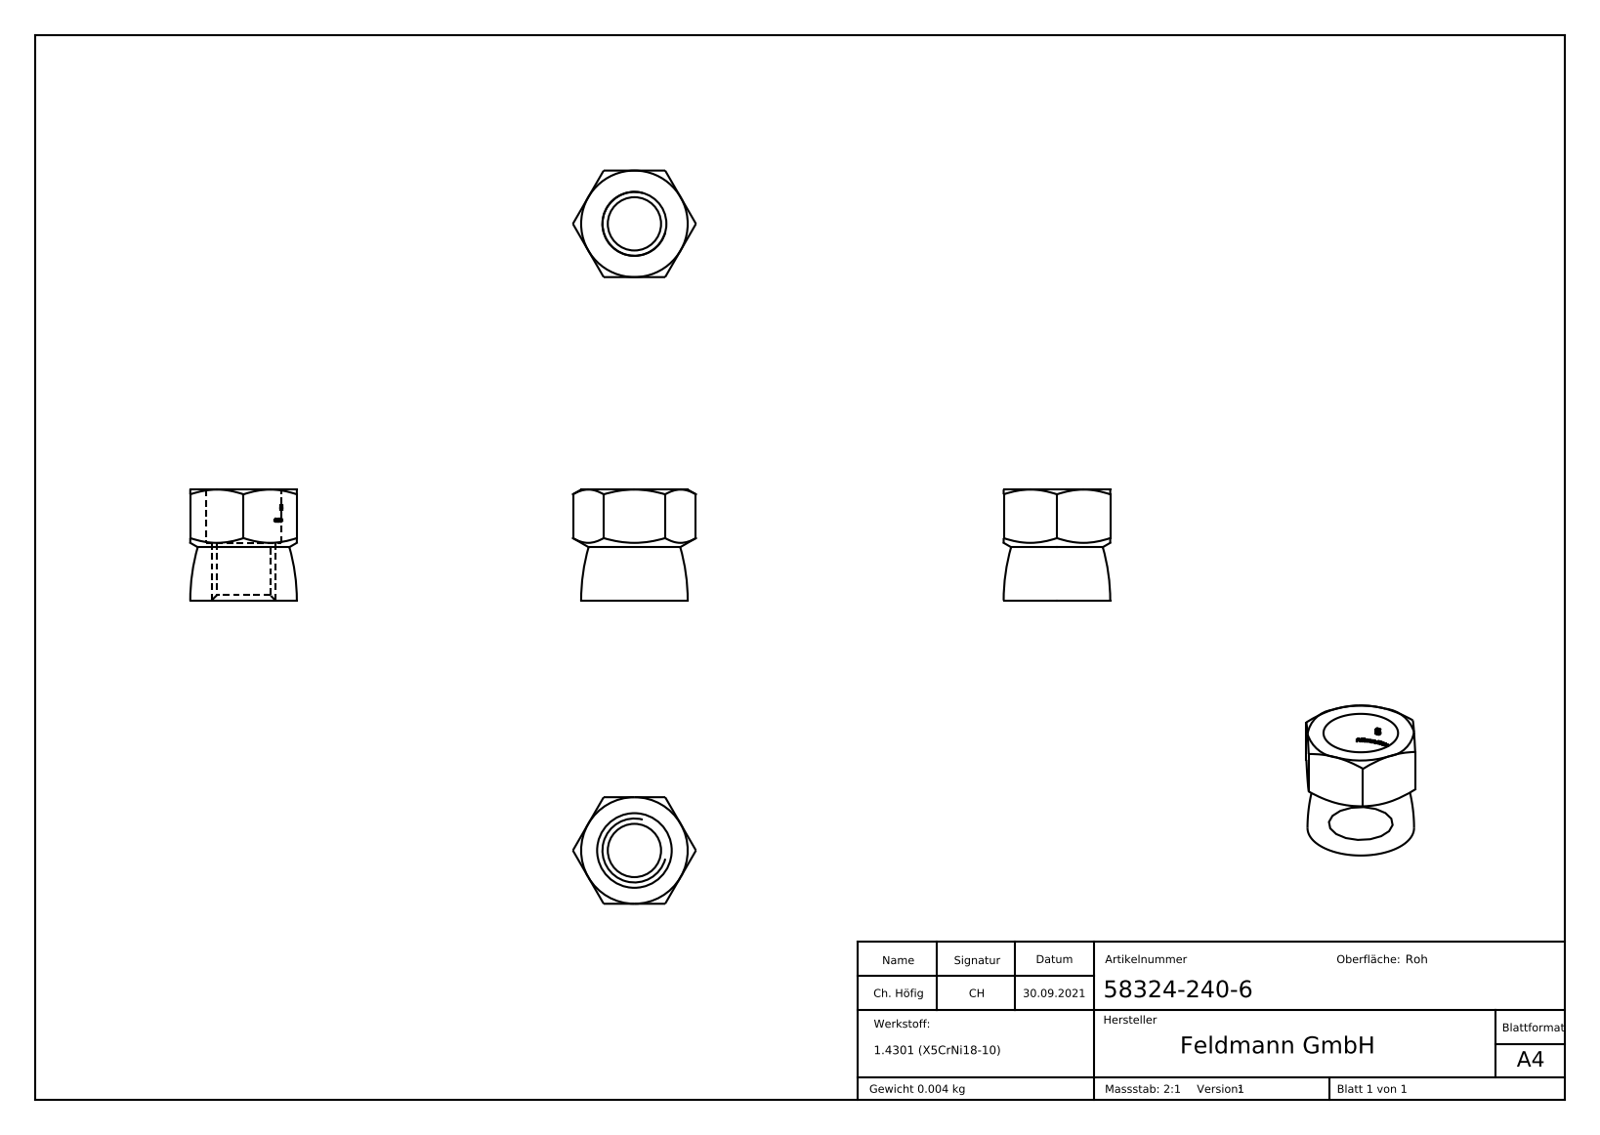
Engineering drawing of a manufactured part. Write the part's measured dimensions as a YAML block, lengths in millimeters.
part_name: "58324-240-6"
step_written_by: "SolidWorks 2018 (CONFIG_CONTROL_DESIGN)"
units: millimeters
bodies: {solids: 1, faces: 320, planar: 143, cylindrical: 31, other: 146}
overall_size: [11.55, 10.4, 10]
volume: 516
surface_area: 668
round_holes:
  - {diameter: 5, count: 1}
  - {diameter: 7, count: 1}
partial_cylinders:
  - {radius: 3.6, count: 1}
face_to_face_distances: [10, 10.4, 5.4, 5, 1.14, 2, 0.44, 1.51, 3, 1.45]
